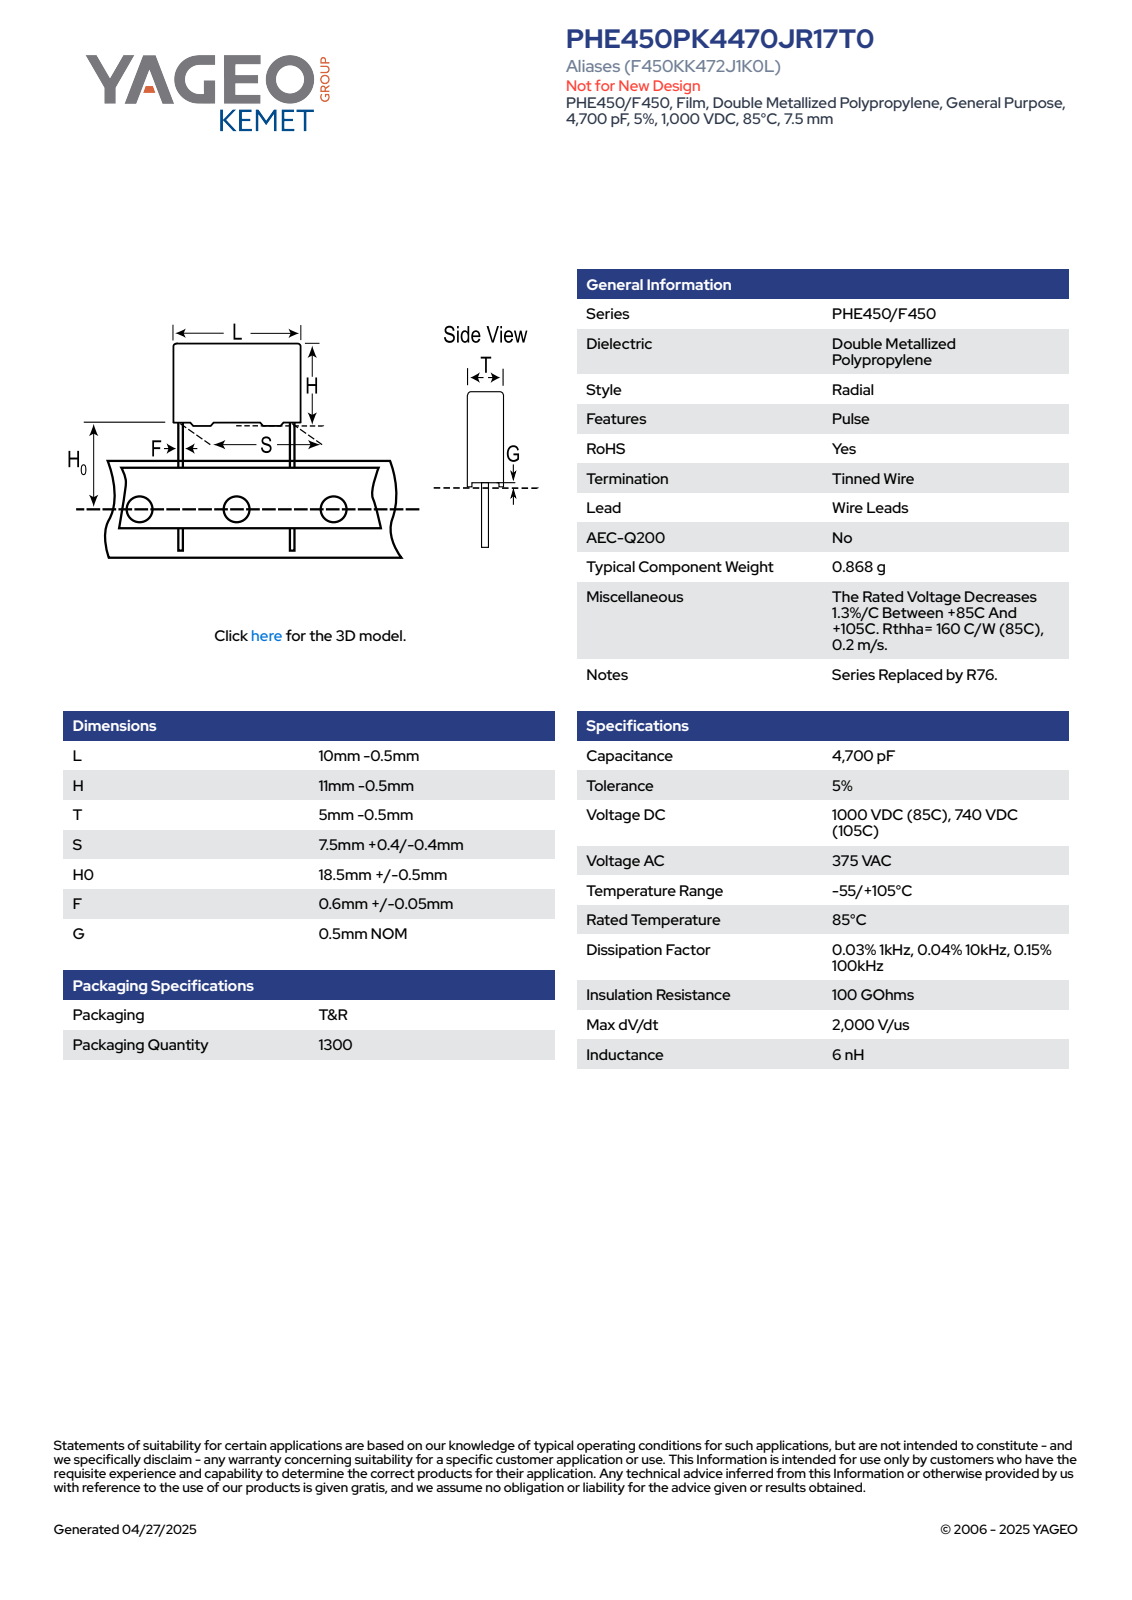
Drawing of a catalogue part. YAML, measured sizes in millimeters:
part_name: "CFR_RBG_10X11X5_L9.5H10.5T4.5S7.5H019F0.65G0.5"
step_written_by: "SolidWorks 2014 (AUTOMOTIVE_DESIGN)"
units: millimeters
bodies: {solids: 4, faces: 89, planar: 81, cylindrical: 8, other: 0}
overall_size: [29.5, 9.5, 4.5]
volume: 440
surface_area: 456
round_bosses_or_shafts:
  - {diameter: 0.65, count: 2}
partial_cylinders:
  - {radius: 0.5, count: 4}
face_to_face_distances: [4.5, 9.5, 10, 4.24, 3.98, 0.5, 10.5, 19, 19.5, 29.5]
